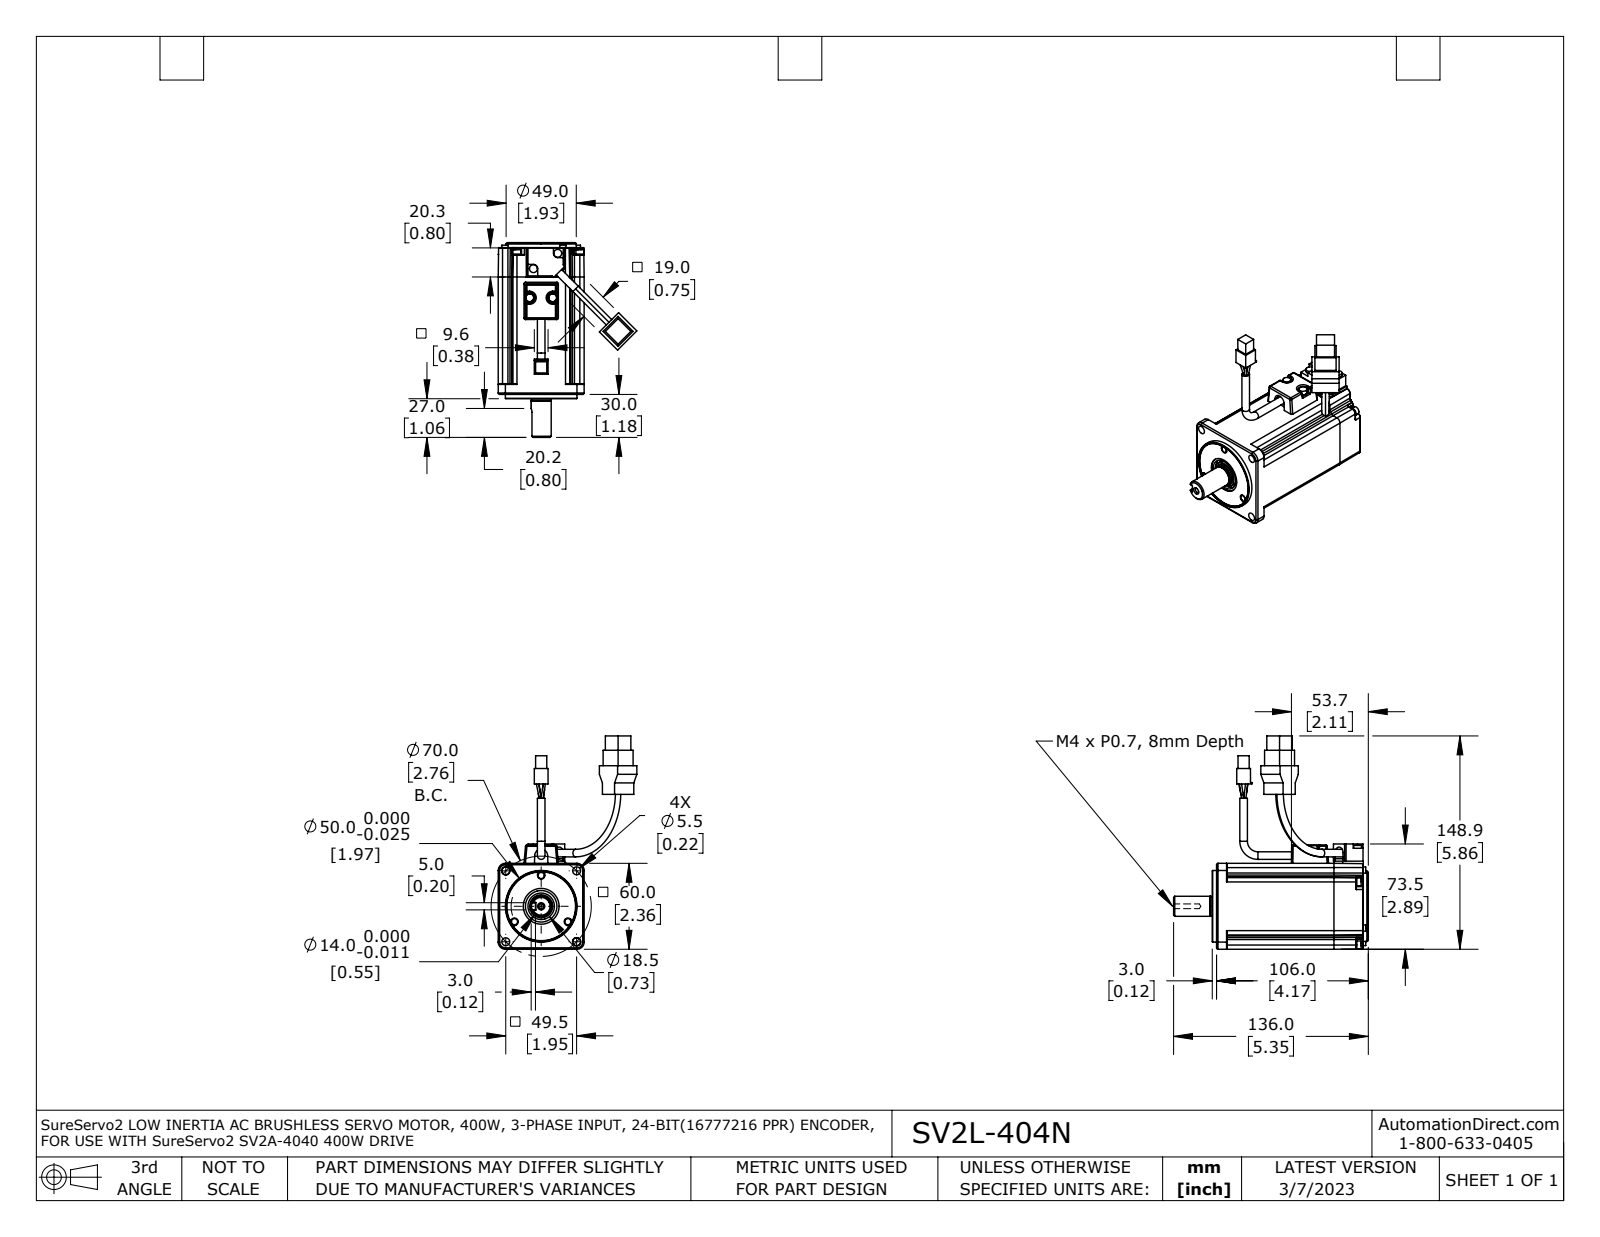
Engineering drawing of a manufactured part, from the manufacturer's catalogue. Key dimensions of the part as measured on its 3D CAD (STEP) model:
Part name (STEP PRODUCT): SV2L-x04N coord
STEP written by: SolidWorks 2021 (AUTOMOTIVE_DESIGN)
Units: inches
Bodies: 1 solid, 607 faces (199 planar, 215 cylindrical, 193 other)
Overall size (bounding box): 5.863 × 5.354 × 3.811
Volume: 22.65 in³ · Surface area: 67.59 in²
Round holes (diameter × count): ⌀0.13 ×4, ⌀0.217 ×2, ⌀0.236 ×1, ⌀0.63 ×1, ⌀0.866 ×1, ⌀0.984 ×1, ⌀1.89 ×1
Round bosses / shafts (diameter × count): ⌀0.217 ×8, ⌀0.169 ×7, ⌀0.228 ×6, ⌀0.209 ×4, ⌀0.059 ×4, ⌀0.118 ×3, ⌀1.969 ×1, ⌀1.929 ×1
Partial cylindrical surfaces — rounded edges, fillets, slot ends (radius × count): R0.039 ×20, R0.079 ×16, R0.006 ×12, R0.012 ×12, R0.118 ×10, R0.02 ×8, R0.087 ×6, R0.197 ×4
Main face-to-face distances: 2.362, 0.394, 0.098, 4.272, 4.173, 1.969, 0.138, 4.134, 4.035, 0.539
Hole centre spacings: 1.378, 0.791, 1.256, 1.646, 2.06, 2.713, 2.756, 2.898
